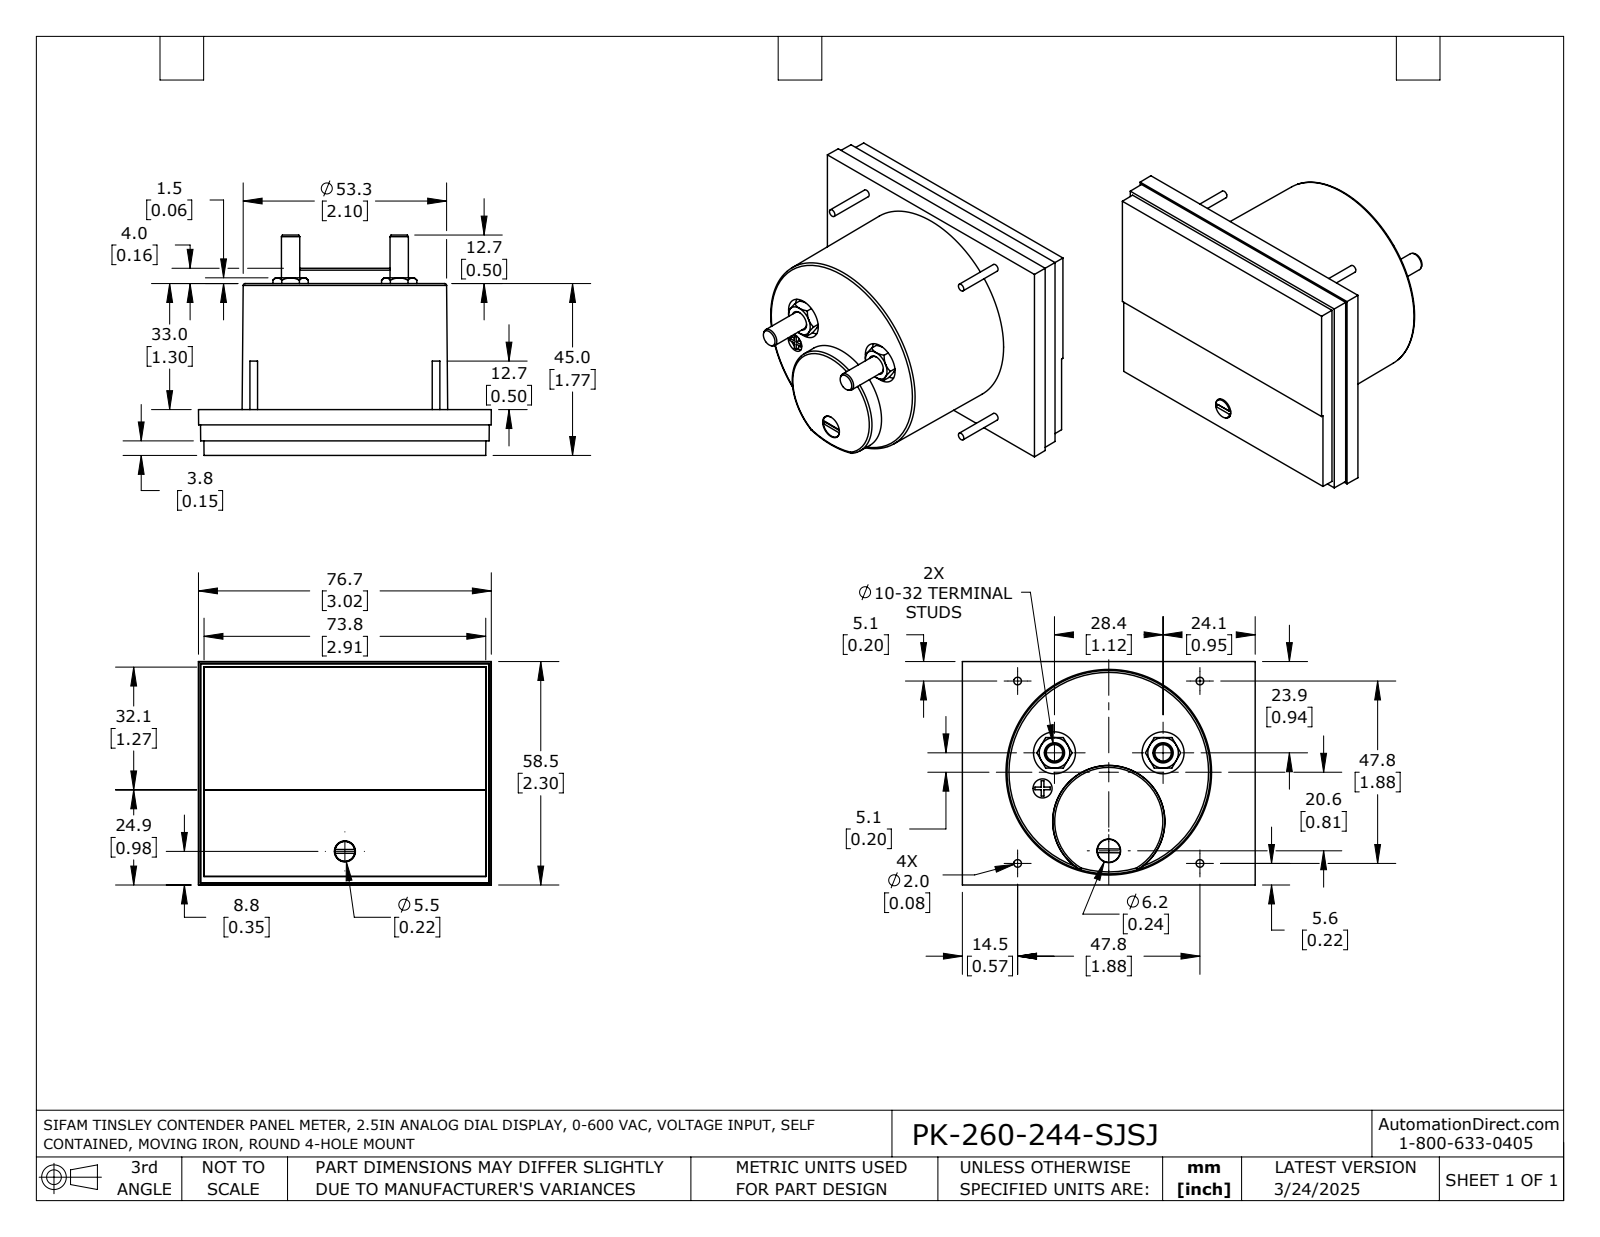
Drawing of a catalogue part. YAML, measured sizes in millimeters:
part_name: "PK-260-244-SJSJ"
step_written_by: "SolidWorks 2021 (AUTOMOTIVE_DESIGN)"
units: millimeters
bodies: {solids: 1, faces: 192, planar: 95, cylindrical: 37, other: 60}
overall_size: [76.7, 58.5, 57.7]
volume: 125500
surface_area: 23580
round_holes:
  - {diameter: 5, count: 3}
  - {diameter: 11, count: 2}
  - {diameter: 5.3, count: 1}
  - {diameter: 5.5, count: 1}
  - {diameter: 6.2, count: 1}
round_bosses_or_shafts:
  - {diameter: 2, count: 4}
  - {diameter: 4.8, count: 2}
  - {diameter: 6, count: 1}
  - {diameter: 5.2, count: 1}
partial_cylinders:
  - {radius: 0.8, count: 1}
face_to_face_distances: [0.5, 12, 3.3, 8.2, 3.8, 11.5, 1.4, 2, 10.1, 1.9]
hole_center_spacings: [29.3, 29.5, 9.8, 23.8, 23.9, 28.4, 32.9]
